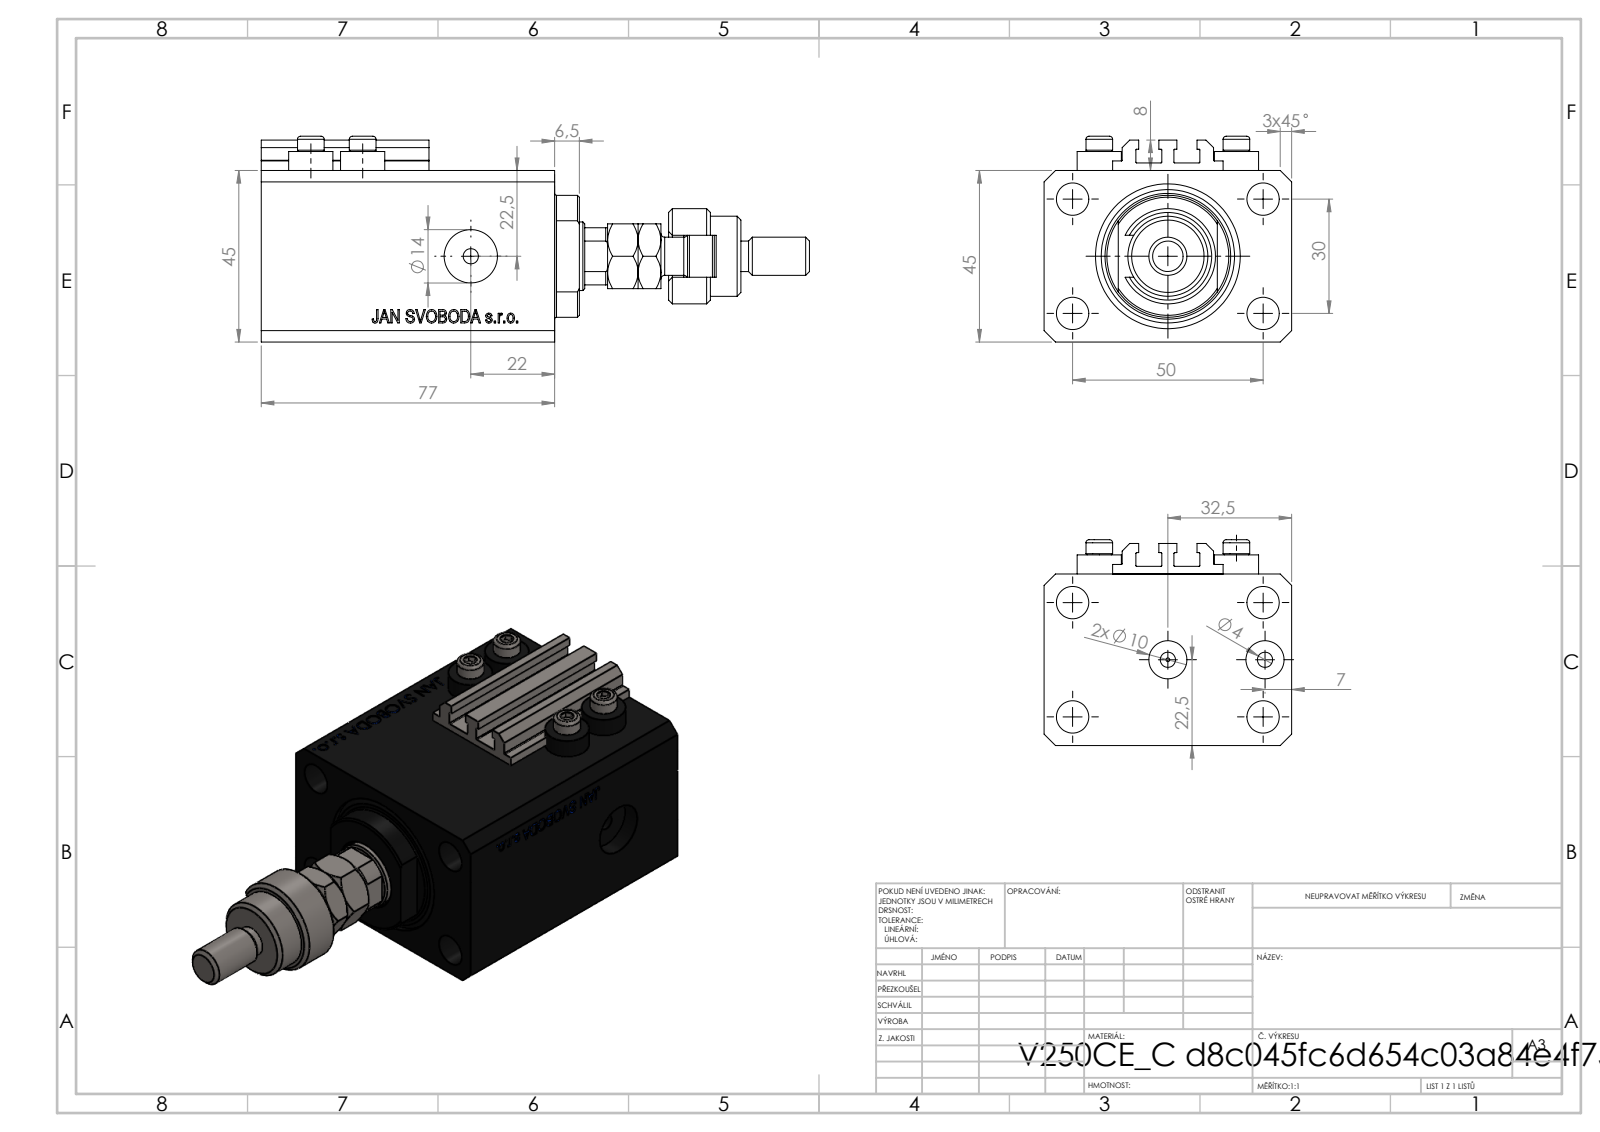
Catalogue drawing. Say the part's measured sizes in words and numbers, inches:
The part is named "V250CE_VC_C; MFA; ALLEN BOLT V250CE; V250CE_C_VCP (+2 more)". Its 3-D file was written by "SolidWorks 2019 (CONFIG_CONTROL_DESIGN)". It is 10 solids with 1127 faces: 532 planar, 105 cylindrical and 490 other. Overall it measures 5.669 by 2.559 by 2.126 inches. Its volume is 13.63 cubic inches and its surface area 97.85 square inches. Round holes: 8 of diameter 0.157, 5 of diameter 0.335, 2 of diameter 0.551, 1 of diameter 0.049, 1 of diameter 0.394, 1 of diameter 0.709, 1 of diameter 1.496. Round bosses or shafts: 4 of diameter 0.457, 4 of diameter 0.276, 1 of diameter 0.984, 1 of diameter 0.827, 1 of diameter 0.63, 1 of diameter 0.394, 1 of diameter 0.315. Partial cylindrical surfaces (rounded edges, fillets, slot ends): 10 of radius 0.008, 1 of radius 0.217, 1 of radius 0.335, 1 of radius 0.344, 1 of radius 0.63. The main face-to-face distances are 1.772, 0.551, 2.559, 2.48, 3.031, 0.118, 0.272, 2.209, 2.76, 1.85. The hole center spacings are 1.148, 0.535, 0.591, 1.181, 1.417, 1.515, 1.969, 2.074.
